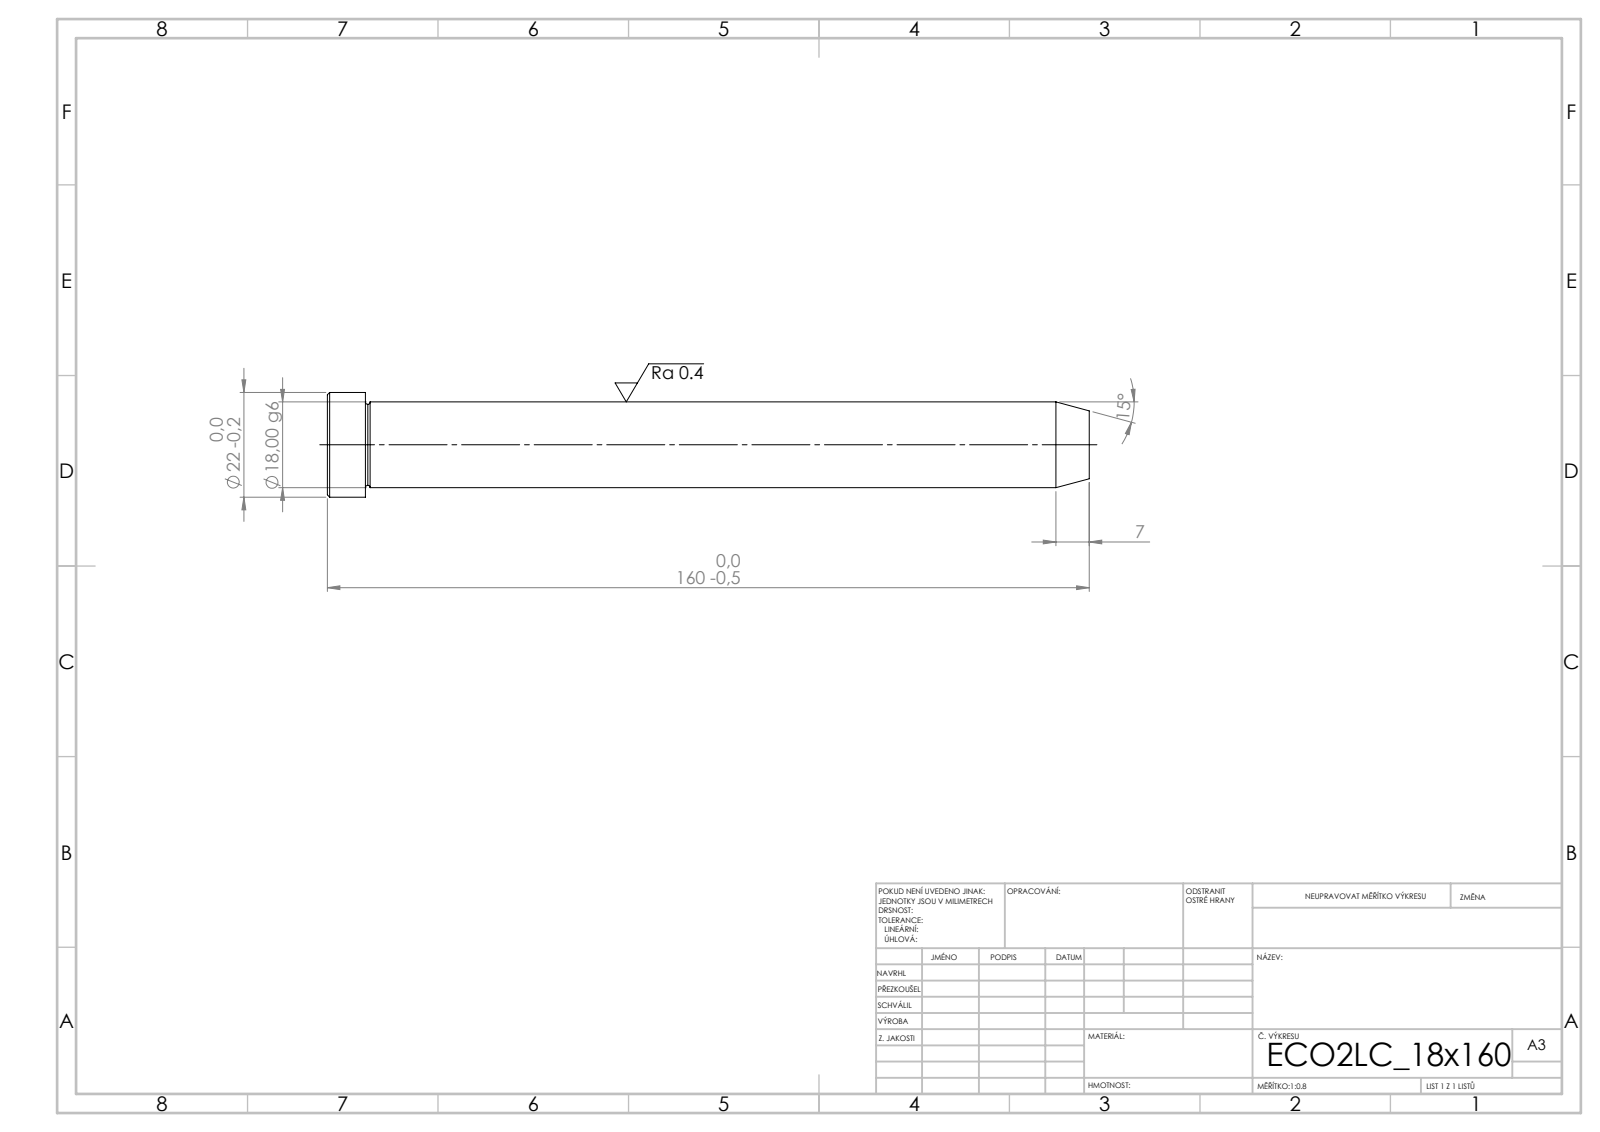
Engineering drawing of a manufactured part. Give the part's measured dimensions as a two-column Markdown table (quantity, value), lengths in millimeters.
| quantity | value |
| --- | --- |
| STEP written by | SolidWorks 2019 (CONFIG_CONTROL_DESIGN) |
| units | millimeters |
| bodies | 1 solid, 15 faces (3 planar, 4 cylindrical, 8 other) |
| overall size | 160 × 22 × 22 |
| volume | 41 345 mm³ |
| surface area | 9 793 mm² |
| round bosses / shafts (diameter × count) | 22 × 1, 18 × 1 |
| main face-to-face distances | 160, 152, 8 |
